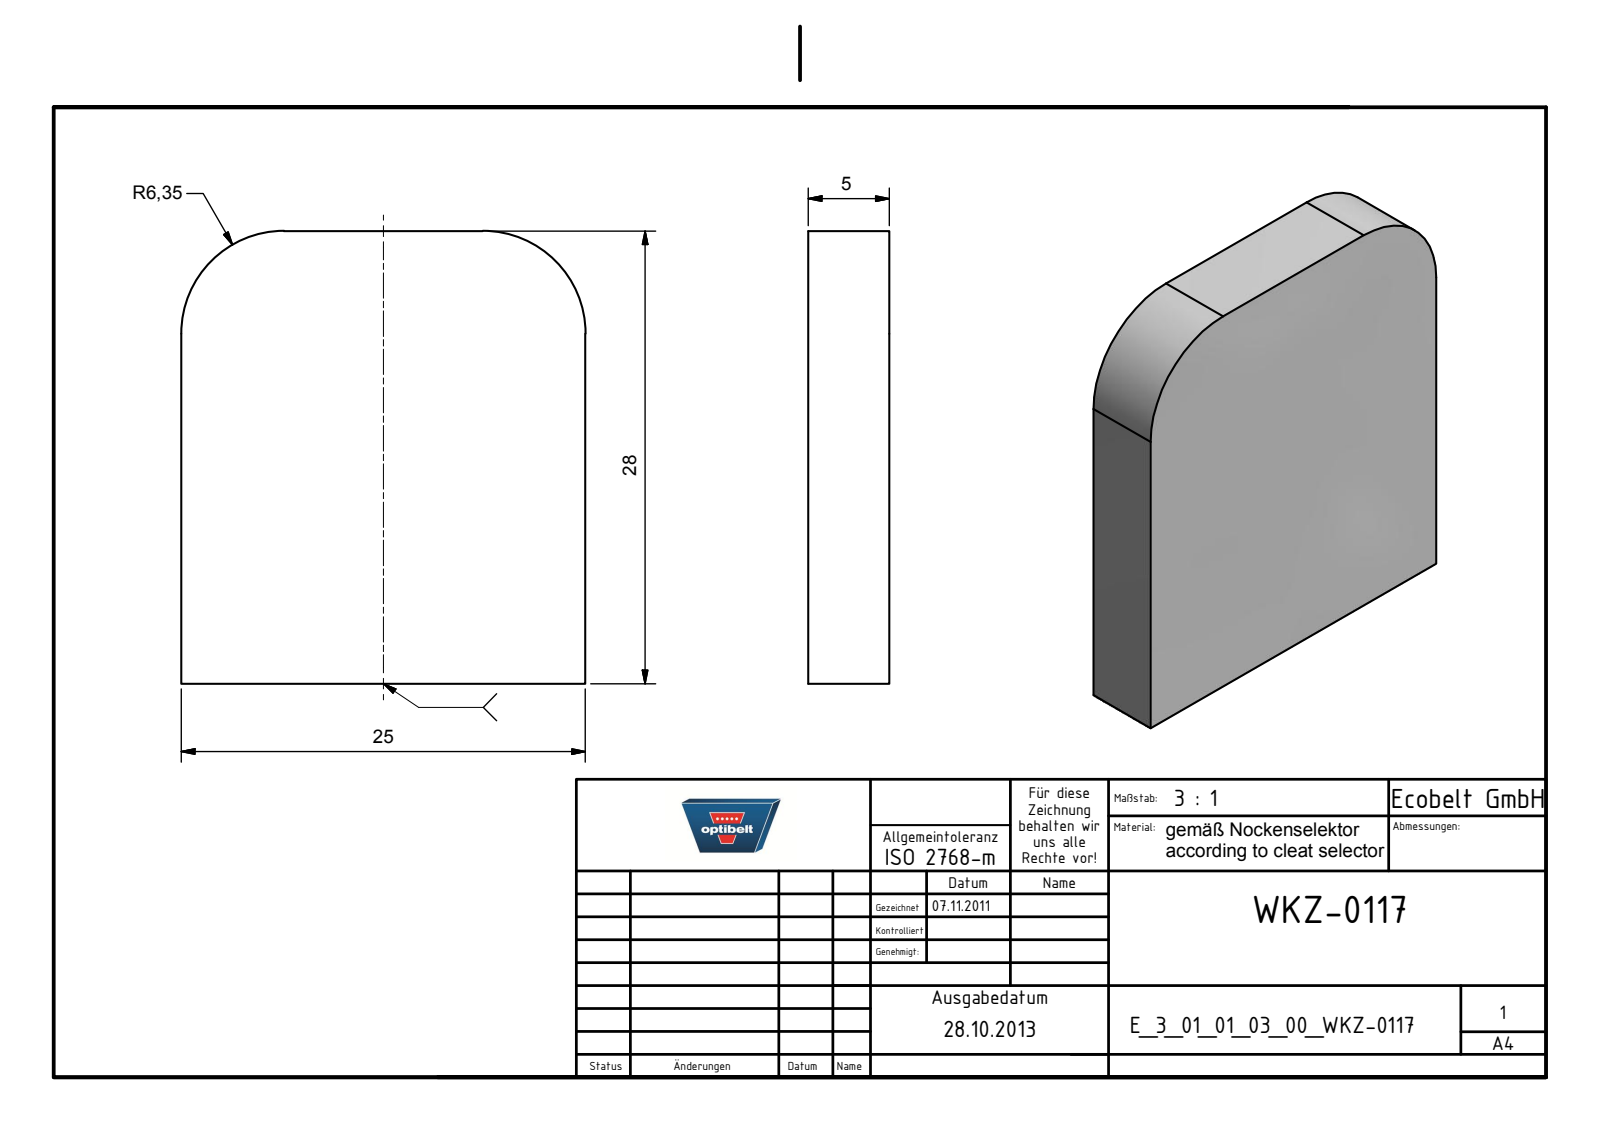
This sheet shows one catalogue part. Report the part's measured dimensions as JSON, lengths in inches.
{"part_name": "E_3_01_01_03_00_WKZ-0117", "step_written_by": "Autodesk Inventor 2021 (AUTOMOTIVE_DESIGN)", "units": "inches", "bodies": {"solids": 1, "faces": 8, "planar": 6, "cylindrical": 2, "other": 0}, "overall_size": [1.102, 0.984, 0.197], "volume_in3": 0.208, "surface_area_in2": 2.895, "partial_cylinders_radius": [[0.25, 2]], "face_to_face_distances": [0.197, 0.984, 1.102]}
